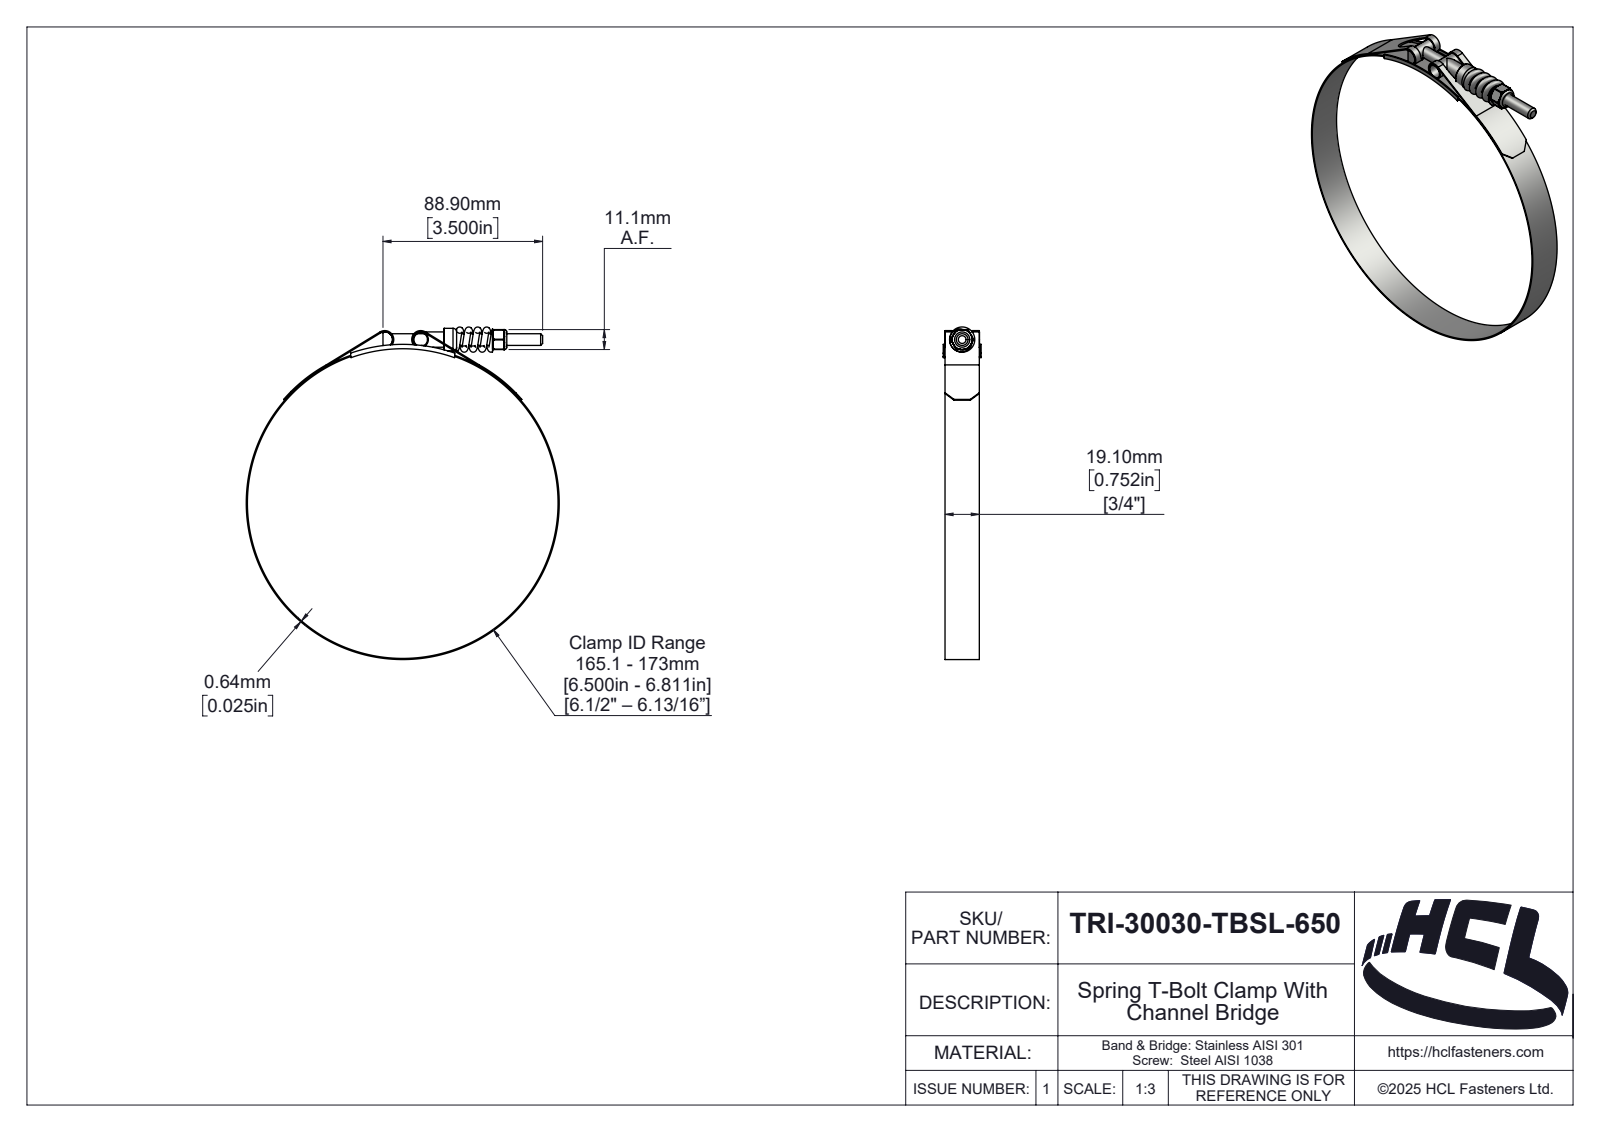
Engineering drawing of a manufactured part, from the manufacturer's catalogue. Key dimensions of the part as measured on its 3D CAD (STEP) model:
Part name (STEP PRODUCT): TRI-30030-TBSL-650
STEP written by: SolidWorks 2025 (AUTOMOTIVE_DESIGN)
Units: millimetres
Bodies: 7 solids, 332 faces (48 planar, 122 cylindrical, 162 other)
Overall size (bounding box): 185.12 × 174.28 × 21.1
Volume: 15 406 mm³ · Surface area: 35 708 mm²
Round holes (diameter × count): ⌀5.4 ×1, ⌀6.35 ×1, ⌀6.5 ×1, ⌀7.52 ×1, ⌀173 ×1
Round bosses / shafts (diameter × count): ⌀8.52 ×2, ⌀174.28 ×1, ⌀12.52 ×1
Partial cylindrical surfaces — rounded edges, fillets, slot ends (radius × count): R0.39 ×6, R0.5 ×2, R4.36 ×2, R5 ×2, R0.59 ×1, R2.42 ×1, R3.03 ×1, R3.19 ×1
Main face-to-face distances: 0.64, 19.1, 1, 20.1, 20.46, 0.36, 19.46, 21.1, 61, 11.11
Hole centre spacings: 91.5
